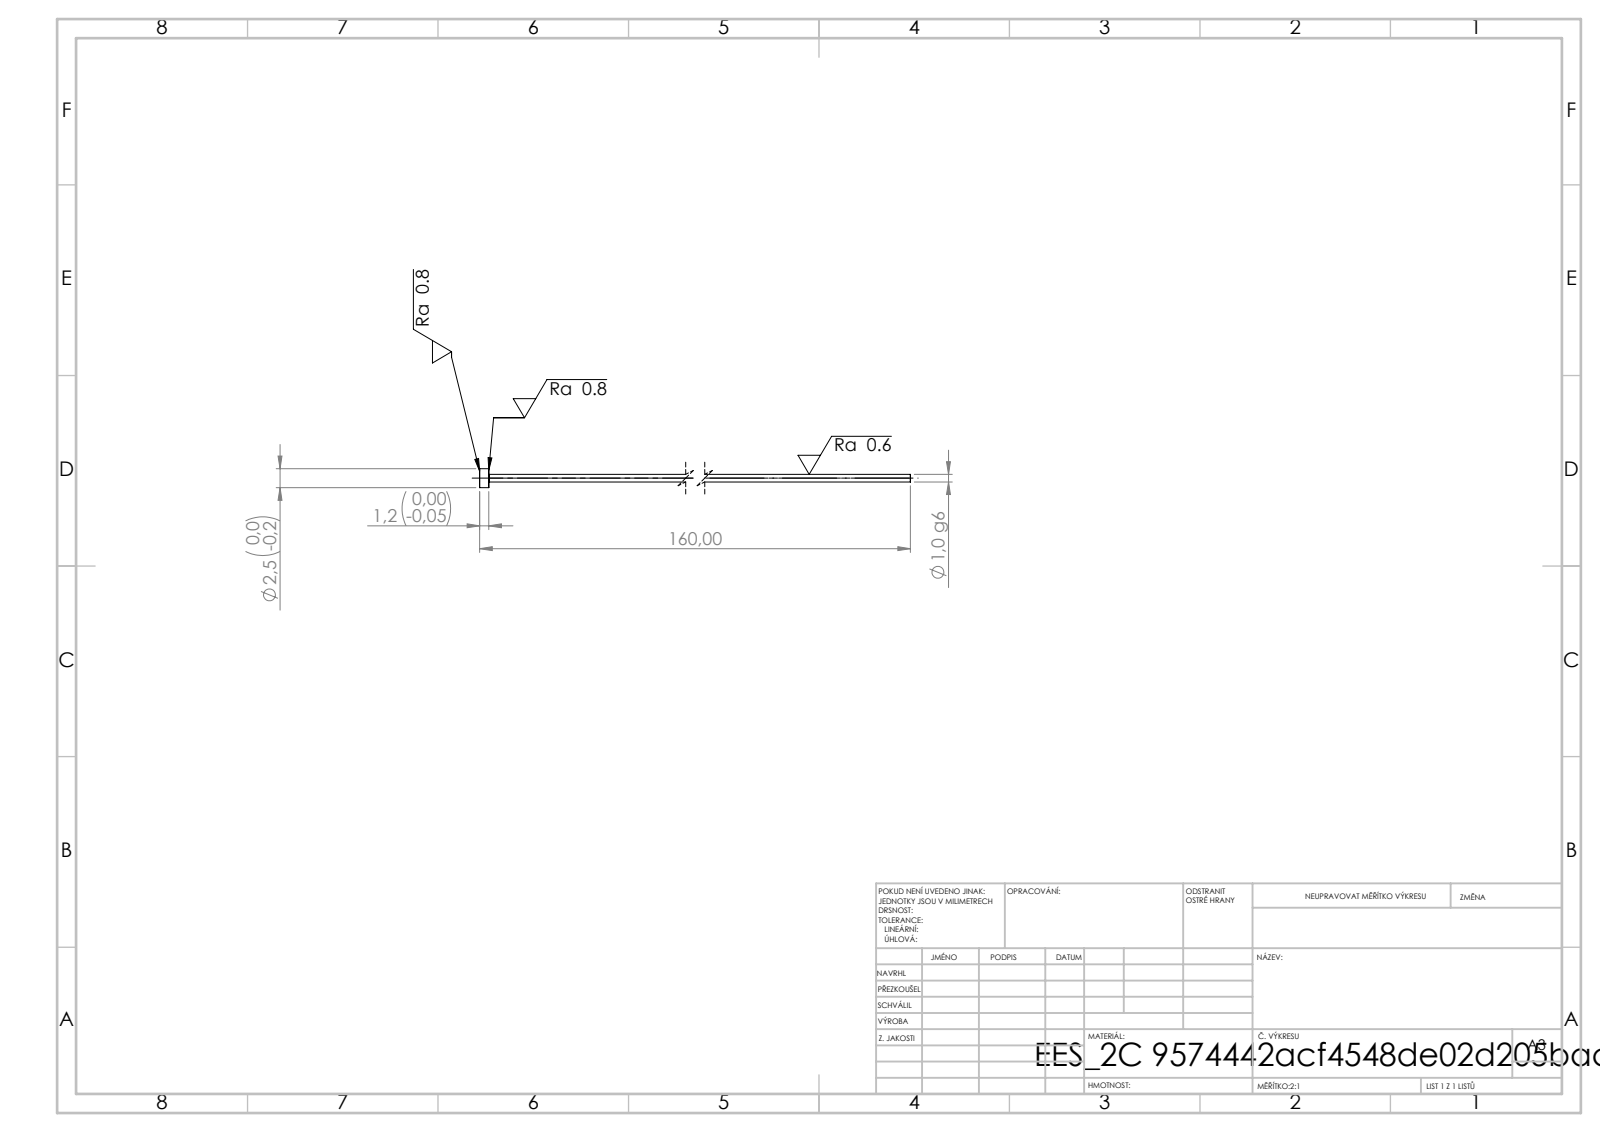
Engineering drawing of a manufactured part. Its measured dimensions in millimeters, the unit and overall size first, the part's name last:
Units: millimetres
Overall size (bounding box): 160 × 2.5 × 2.5
Round bosses / shafts (diameter × count): ⌀2.5 ×1, ⌀1 ×1
Main face-to-face distances: 1.2, 160, 158.8
Volume: 131 mm³ · Surface area: 518 mm²
Bodies: 1 solid, 7 faces (3 planar, 4 cylindrical, 0 other)
STEP written by: SolidWorks 2019 (CONFIG_CONTROL_DESIGN)
